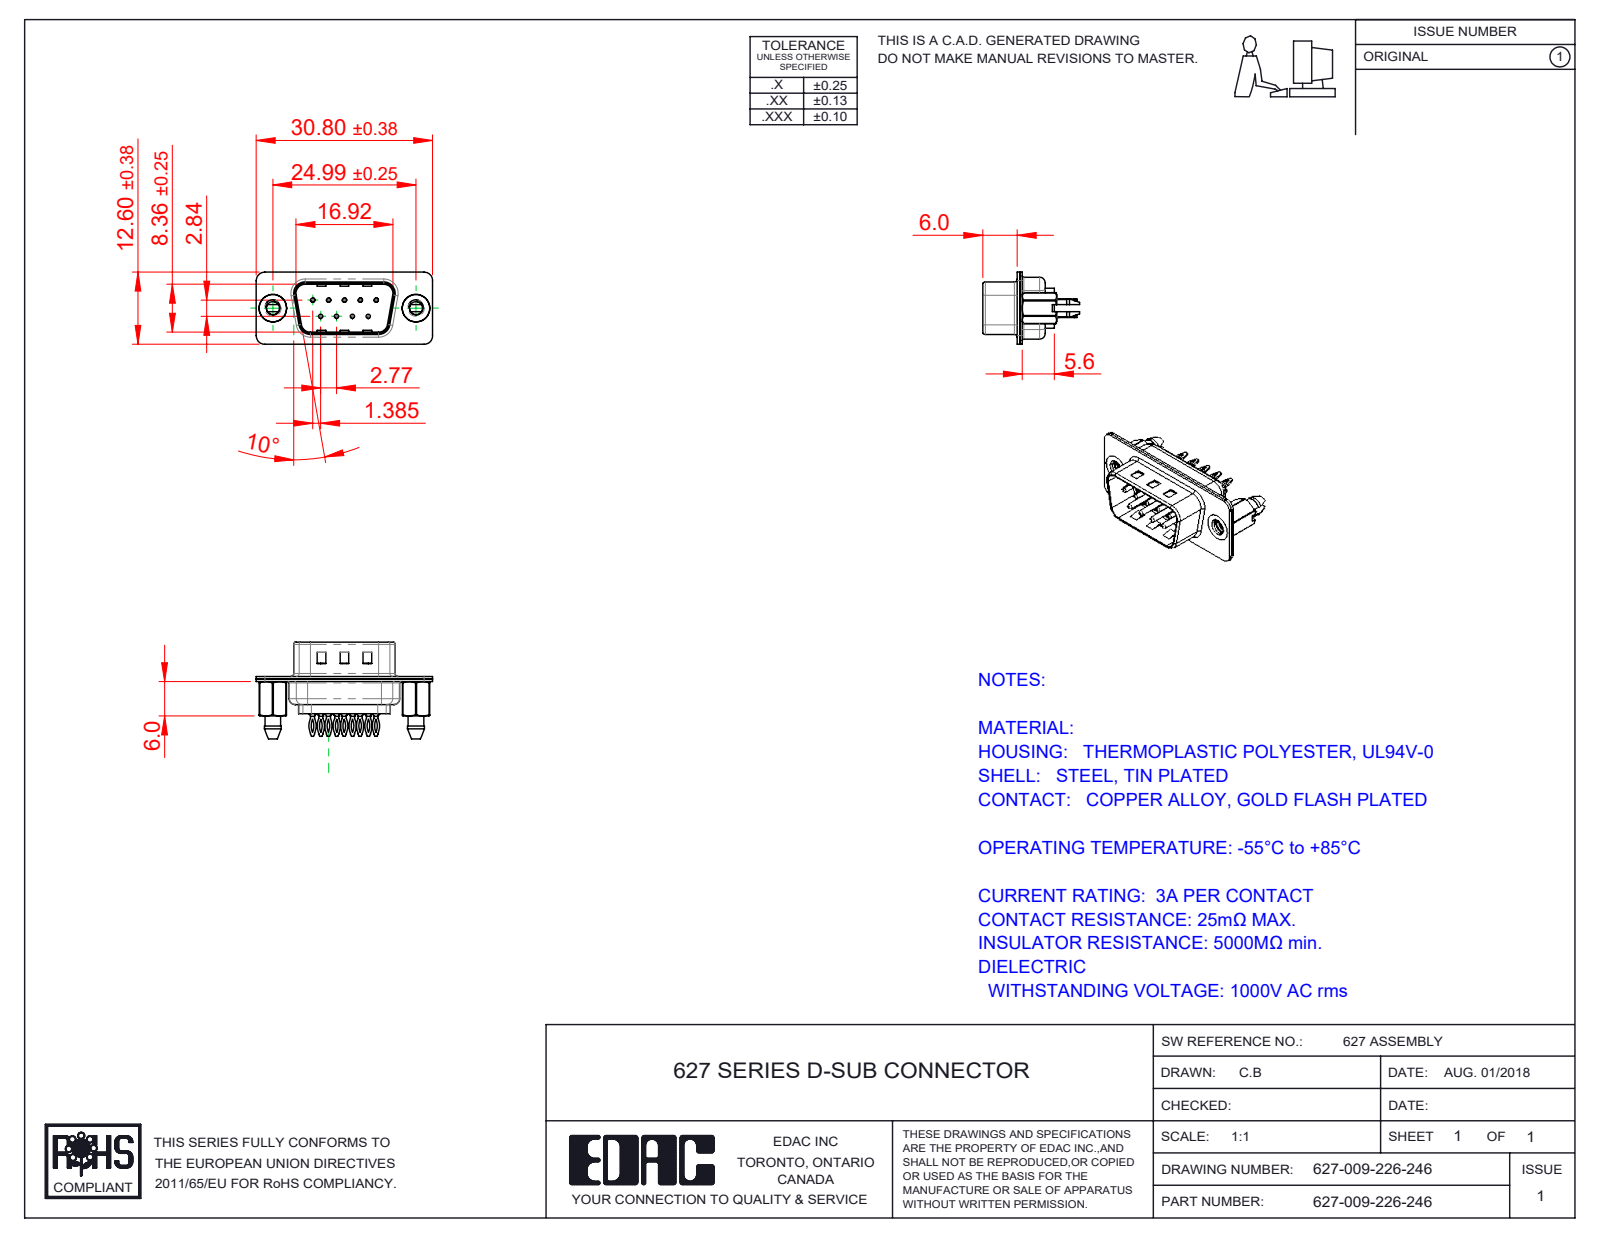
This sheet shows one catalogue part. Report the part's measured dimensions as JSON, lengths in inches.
{"part_name": "627 Contact Row 1_26L; 627 Housing_09 LP; 627 Shell Front_09 Contacts; 627 Contact Row 2_26L (+3 more)", "step_written_by": "SolidWorks 2020 (CONFIG_CONTROL_DESIGN)", "units": "inches", "bodies": {"solids": 14, "faces": 1062, "planar": 319, "cylindrical": 440, "other": 303}, "overall_size": [1.213, 0.665, 0.496], "volume_in3": 0.087, "surface_area_in2": 6.505, "round_holes": [[0.014, 9], [0.043, 9], [0.063, 9], [0.089, 2], [0.157, 2], [0.189, 2]], "round_bosses_or_shafts": [[0.079, 9], [0.059, 9], [0.03, 9], [0.193, 2]], "partial_cylinders_radius": [[0.059, 20], [0.115, 18], [0.131, 18], [0.079, 12], [0.063, 10], [0.02, 8], [0.01, 4], [0.024, 4]], "face_to_face_distances": [0.016, 0.018, 0.035, 0.032, 0.377, 0.055, 0.345, 0.256, 0.02, 0.059], "hole_center_spacings": [0.124, 0.109, 0.218, 0.198, 0.198, 0.327, 0.294, 0.295]}
